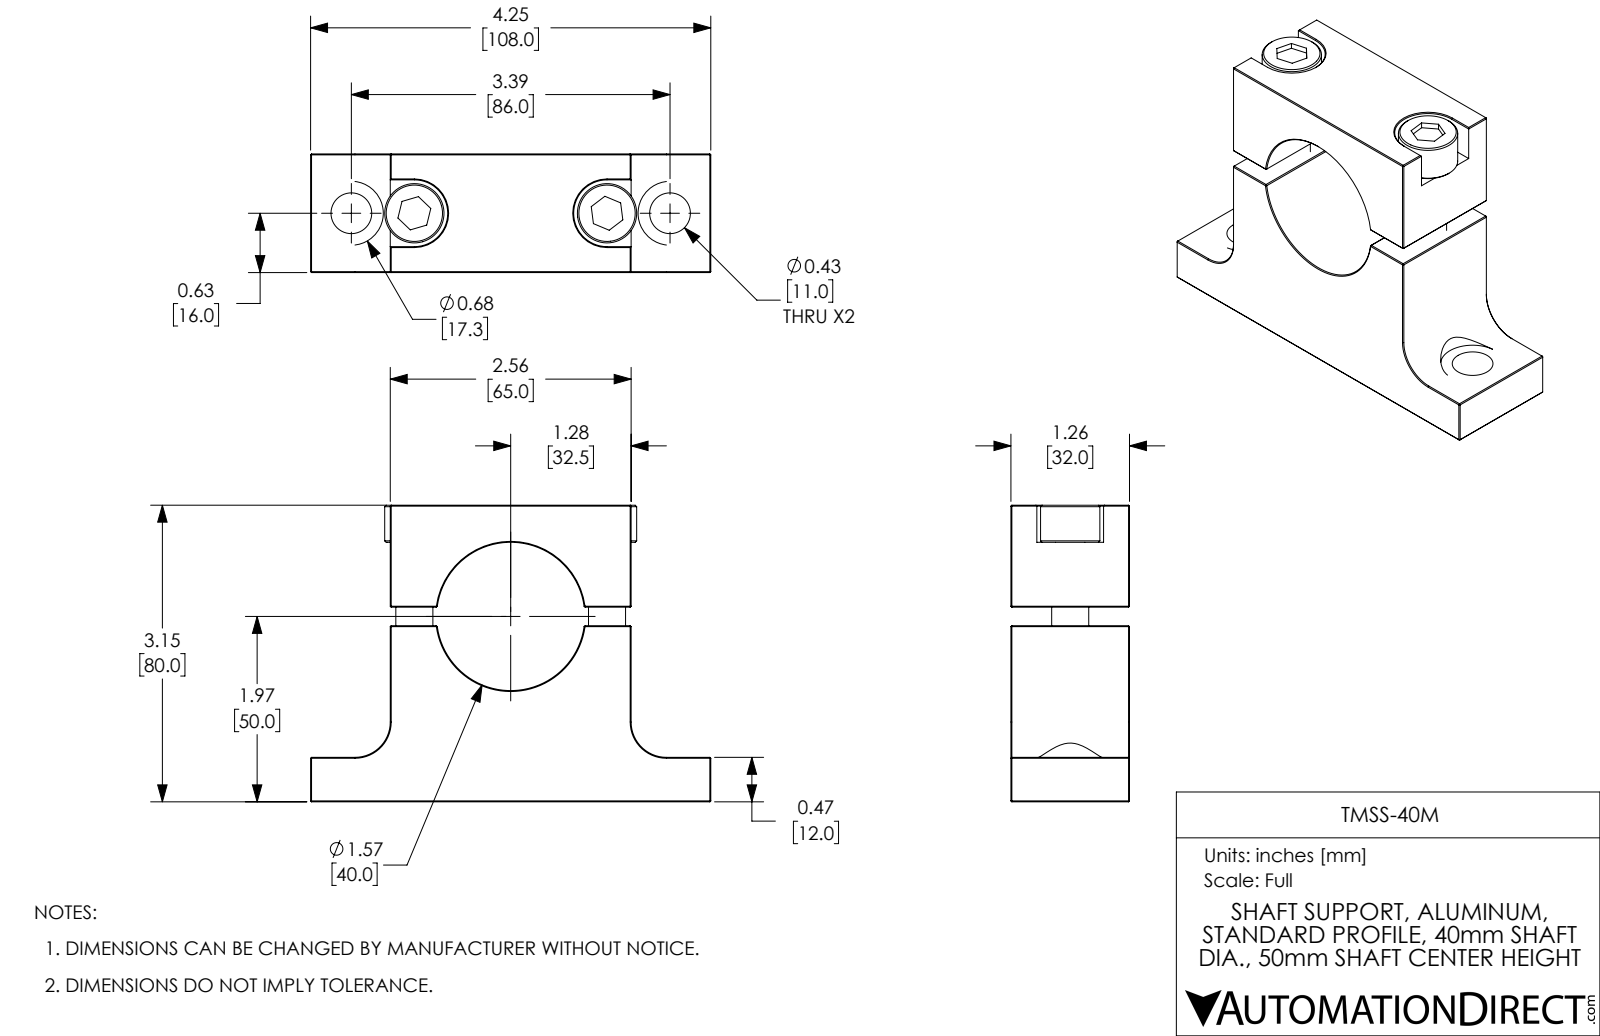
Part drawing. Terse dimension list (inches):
name: TMSS-40M
written by: SolidWorks 2017 (AUTOMOTIVE_DESIGN)
unit: in
bodies: 4 solids, 176 faces (120 planar, 32 cylindrical, 24 other)
size: 4.252 × 3.15 × 1.26
volume: 8.135 in³; area: 51.82 in²
holes: 2× ⌀0.33, 2× ⌀0.433, 2× ⌀0.433, 1× ⌀0.094, 1× ⌀1.575
bosses: 2× ⌀0.63, 2× ⌀0.394
rounds: 2× R0.34, 2× R0.354, 2× R0.375
face distances: 1.26, 3.15, 2.559, 0.472, 2.677, 0.846, 3.406, 1.87, 1.398, 1.28
hole spacings: 0.669, 1.024, 1.693, 2.717, 2.047, 3.386
